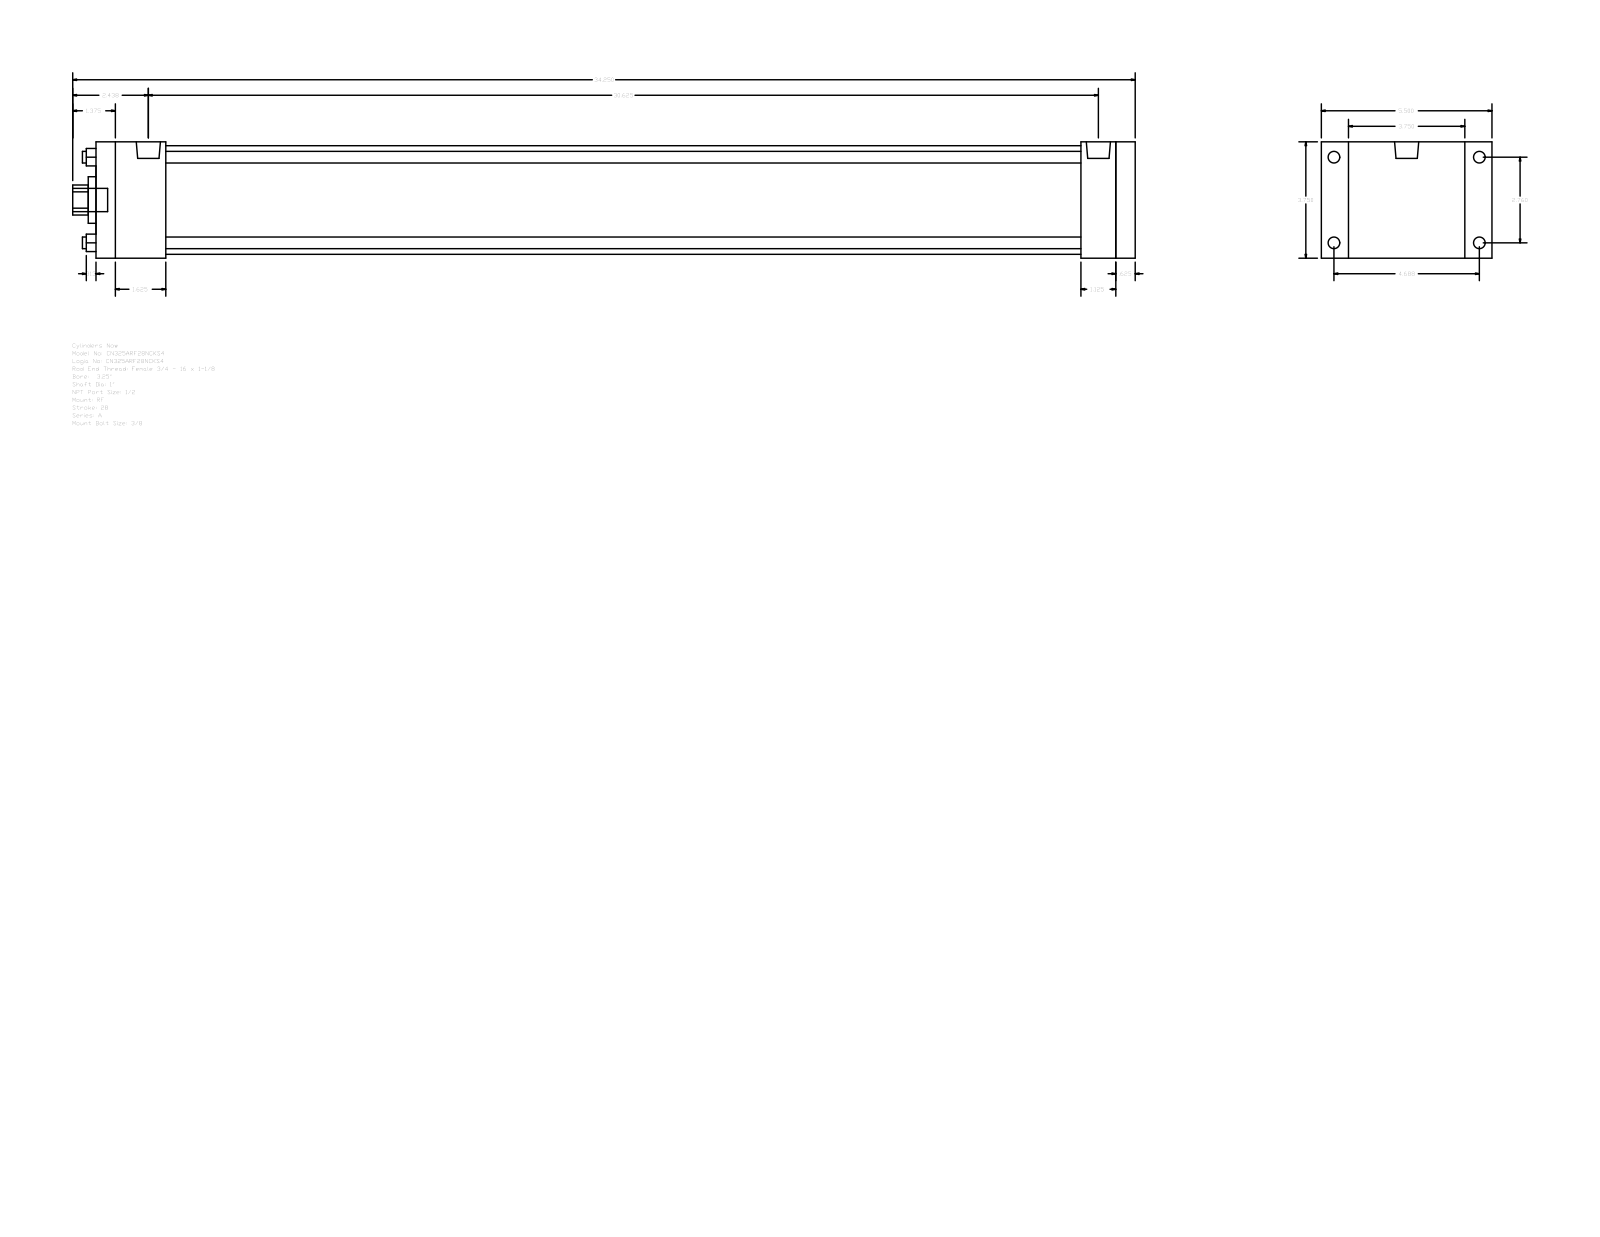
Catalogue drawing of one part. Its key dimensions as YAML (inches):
part_name: "A_RF__0325_1"
step_written_by: "GSSL Pune (CONFIG_CONTROL_DESIGN)"
units: inches
bodies: {solids: 0, faces: 92, planar: 64, cylindrical: 28, other: 0}
overall_size: [34.25, 5.5, 3.75]
round_holes:
  - {diameter: 0.375, count: 4}
  - {diameter: 1, count: 1}
  - {diameter: 1.5, count: 1}
  - {diameter: 3.5, count: 1}
round_bosses_or_shafts:
  - {diameter: 0.375, count: 4}
  - {diameter: 0.344, count: 4}
  - {diameter: 0.778, count: 2}
  - {diameter: 0.75, count: 1}
partial_cylinders:
  - {radius: 0.484, count: 1}
face_to_face_distances: [3.75, 33.5, 0.625, 32.875, 0.875, 4.625, 31.75, 1.125, 1.75, 2.25]
hole_center_spacings: [1.952, 2.76, 3.903]
